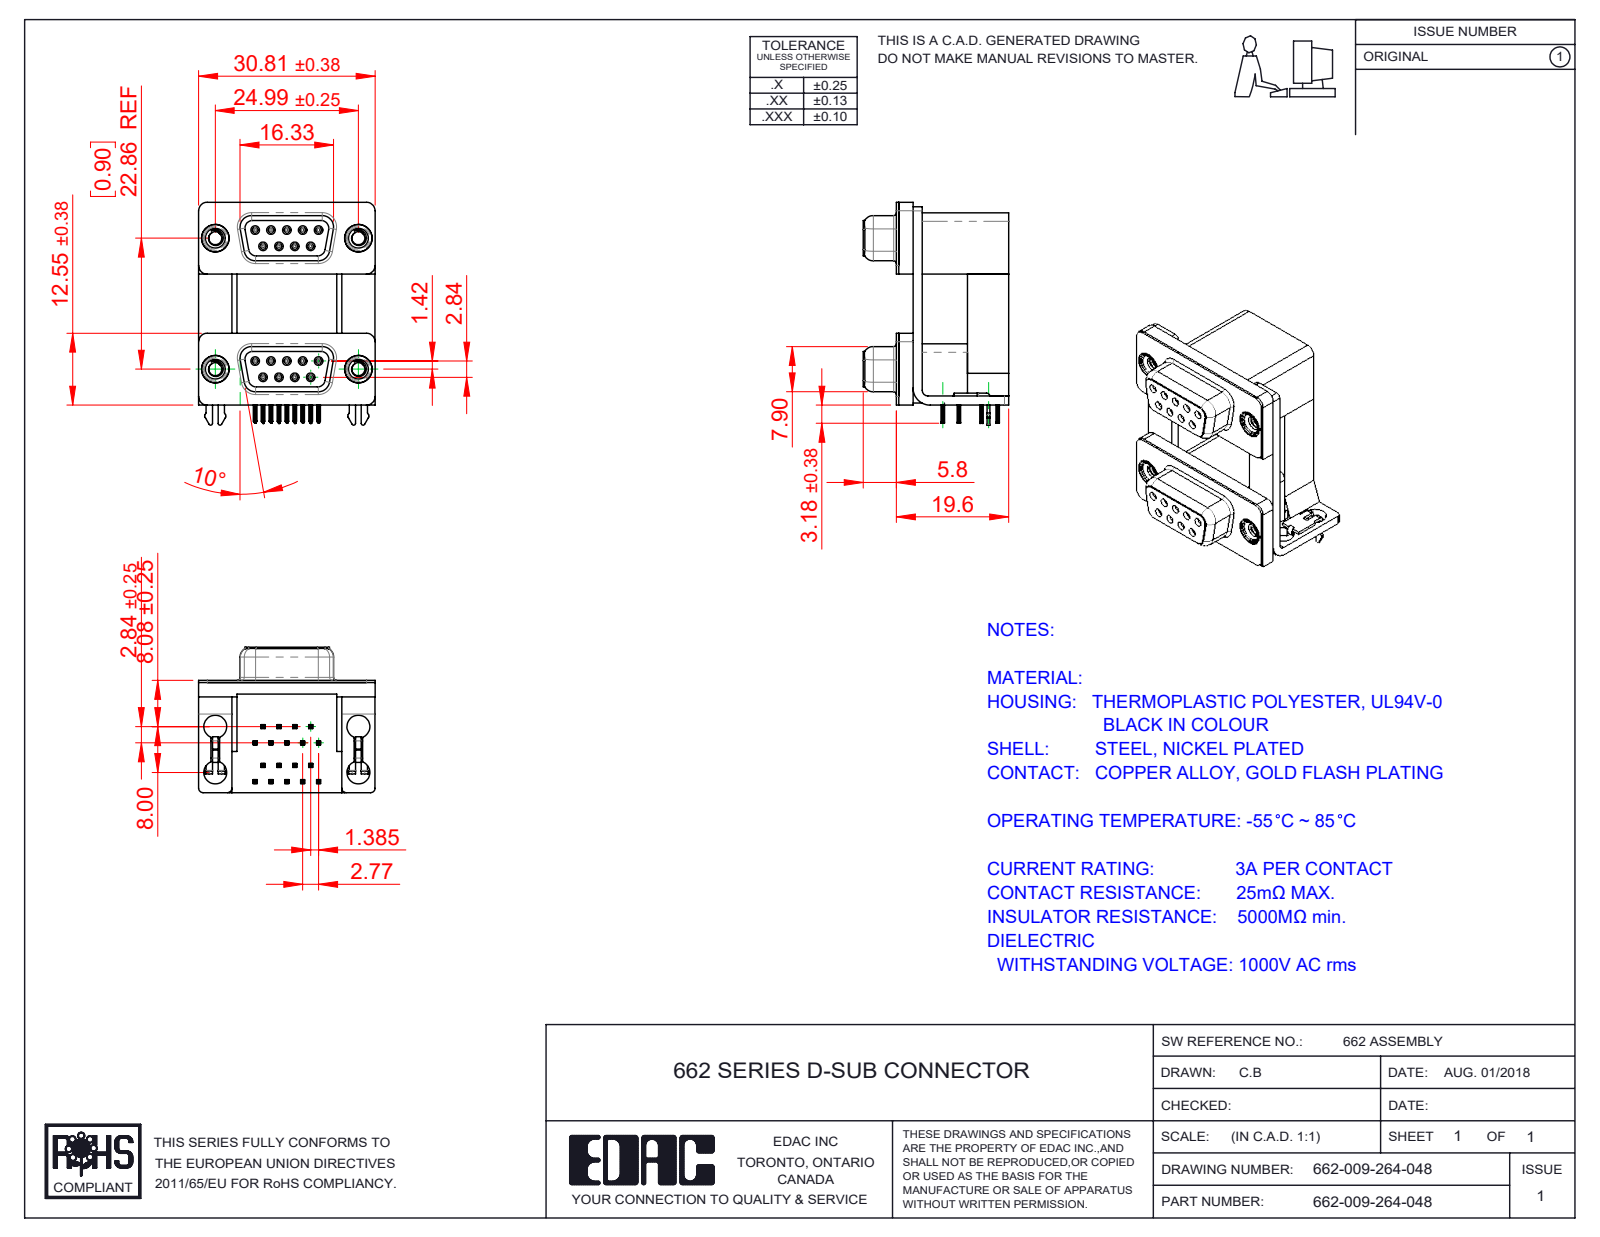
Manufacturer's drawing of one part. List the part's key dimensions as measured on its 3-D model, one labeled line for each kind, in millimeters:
Part name (STEP PRODUCT): 662 Shell_09 Contacts; 662-009-264-048; 662 Contact Bottom Lower; 662 2 Prong Board Lock_4 (+8 more)
STEP written by: SolidWorks 2020 (CONFIG_CONTROL_DESIGN)
Units: millimetres
Bodies: 31 solids, 3218 faces (1452 planar, 826 cylindrical, 940 other)
Overall size (bounding box): 38.91 × 30.81 × 25.4
Volume: 11 834 mm³ · Surface area: 13 881 mm²
Round holes (diameter × count): ⌀0.8 ×18, ⌀0.9 ×18, ⌀4 ×8, ⌀2.26 ×4, ⌀3.5 ×4, ⌀4.8 ×4, ⌀5 ×4
Round bosses / shafts (diameter × count): ⌀1.2 ×18, ⌀4.9 ×4, ⌀4.75 ×4, ⌀3.9 ×4
Partial cylindrical surfaces — rounded edges, fillets, slot ends (radius × count): R0.1 ×145, R0.15 ×72, R0.35 ×36, R0.34 ×18, R1.35 ×16, R1.5 ×13, R0.5 ×12, R0.75 ×10
Main face-to-face distances: 2.5, 16.7, 19.2, 0.4, 22.86, 9.5, 7.2, 12, 2.9, 1.6
Hole centre spacings: 3.16, 2.77, 23.03, 22.86, 5.54, 23.52, 20.07, 25.74
